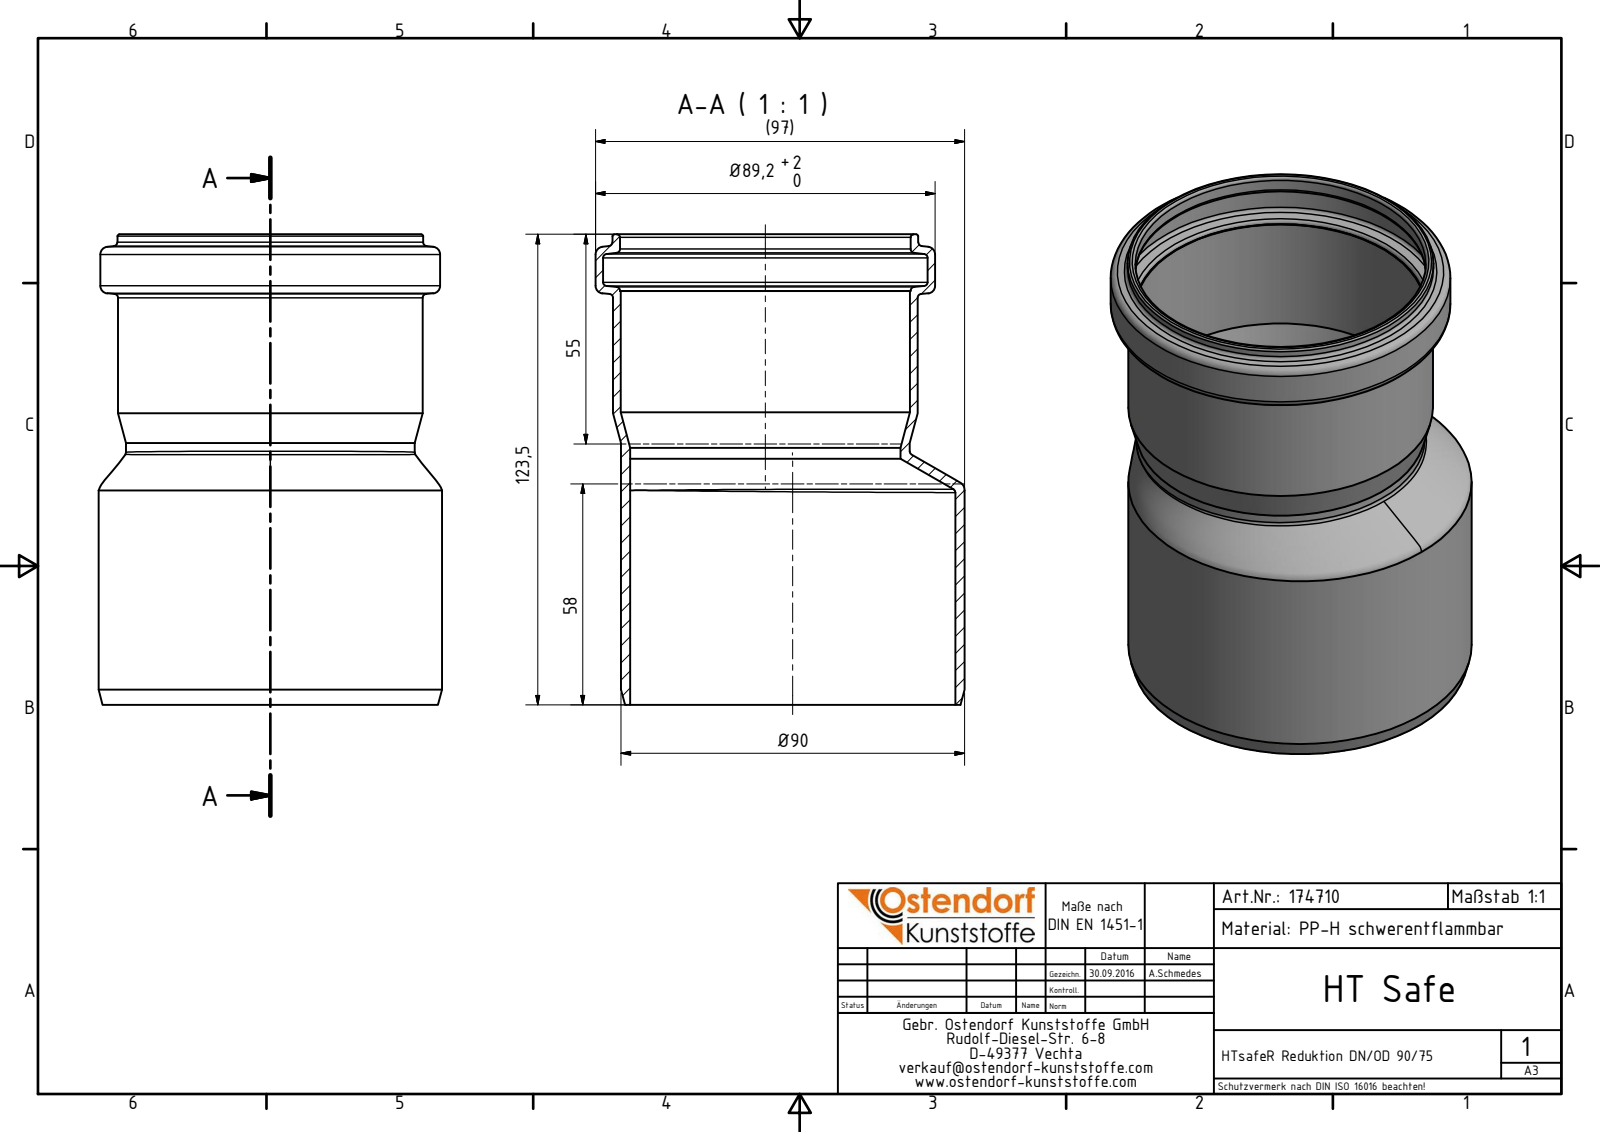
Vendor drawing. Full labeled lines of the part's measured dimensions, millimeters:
Part name (STEP PRODUCT): 174710 HTsafeR DN_OD 90_75
STEP written by: Autodesk Inventor 2016 (AUTOMOTIVE_DESIGN)
Units: millimetres
Bodies: 1 solid, 35 faces (3 planar, 11 cylindrical, 21 other)
Overall size (bounding box): 123.5 × 96.9 × 90.2
Volume: 77 390 mm³ · Surface area: 70 463 mm²
Round holes (diameter × count): ⌀71 ×1, ⌀76 ×1, ⌀76.3 ×1, ⌀85.2 ×1, ⌀85.4 ×1
Round bosses / shafts (diameter × count): ⌀90.2 ×1, ⌀89.2 ×1, ⌀80.3 ×1, ⌀80 ×1, ⌀75.8 ×1
Main face-to-face distances: 123.5, 108.61, 14.89
Hole centre spacings: 7.2
